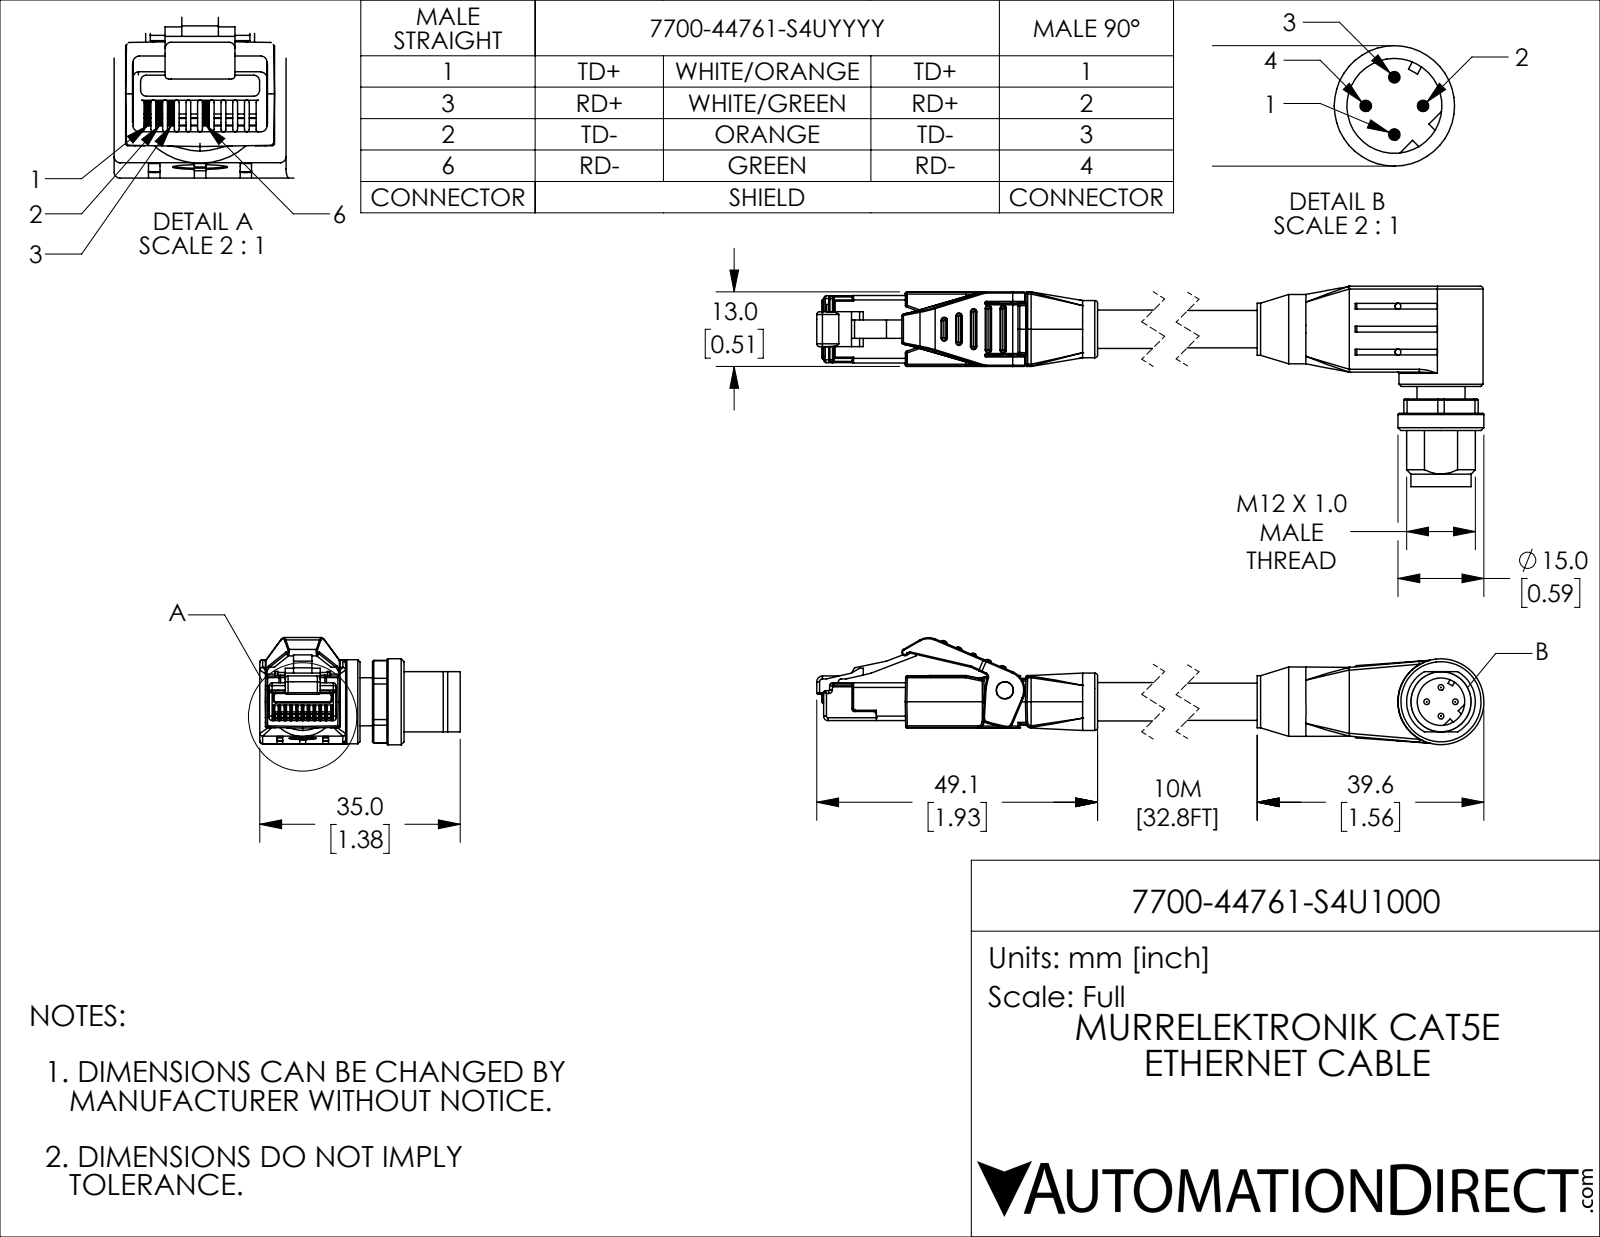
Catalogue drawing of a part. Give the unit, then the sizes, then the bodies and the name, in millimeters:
Units: millimetres
Overall size (bounding box): 146.8 × 35 × 18.7
Round holes (diameter × count): ⌀1 ×4, ⌀3 ×1, ⌀4.8 ×1, ⌀8.3 ×1
Round bosses / shafts (diameter × count): ⌀1 ×4, ⌀15 ×1, ⌀14.7 ×1, ⌀12.1 ×1, ⌀10.5 ×1, ⌀10 ×1, ⌀9.1 ×1, ⌀8.4 ×1
Partial cylindrical surfaces — rounded edges, fillets, slot ends (radius × count): R0.2 ×82, R0.3 ×67, R0.5 ×28, R0.1 ×20, R0.8 ×5, R1 ×5, R2 ×2, R5 ×2
Main face-to-face distances: 13, 9.2, 1, 17.5, 2.5, 14, 15, 4.7, 2, 8.6
Hole centre spacings: 8, 106.4
Volume: 15 000 mm³ · Surface area: 7 626 mm²
Bodies: 3 solids, 883 faces (369 planar, 338 cylindrical, 176 other)
Part name (STEP PRODUCT): 7700-44761-S4U1000_2; 7700-44761-S4U1000; 7700-44761-S4U1000_1
STEP written by: SolidWorks 2021 (CONFIG_CONTROL_DESIGN)
